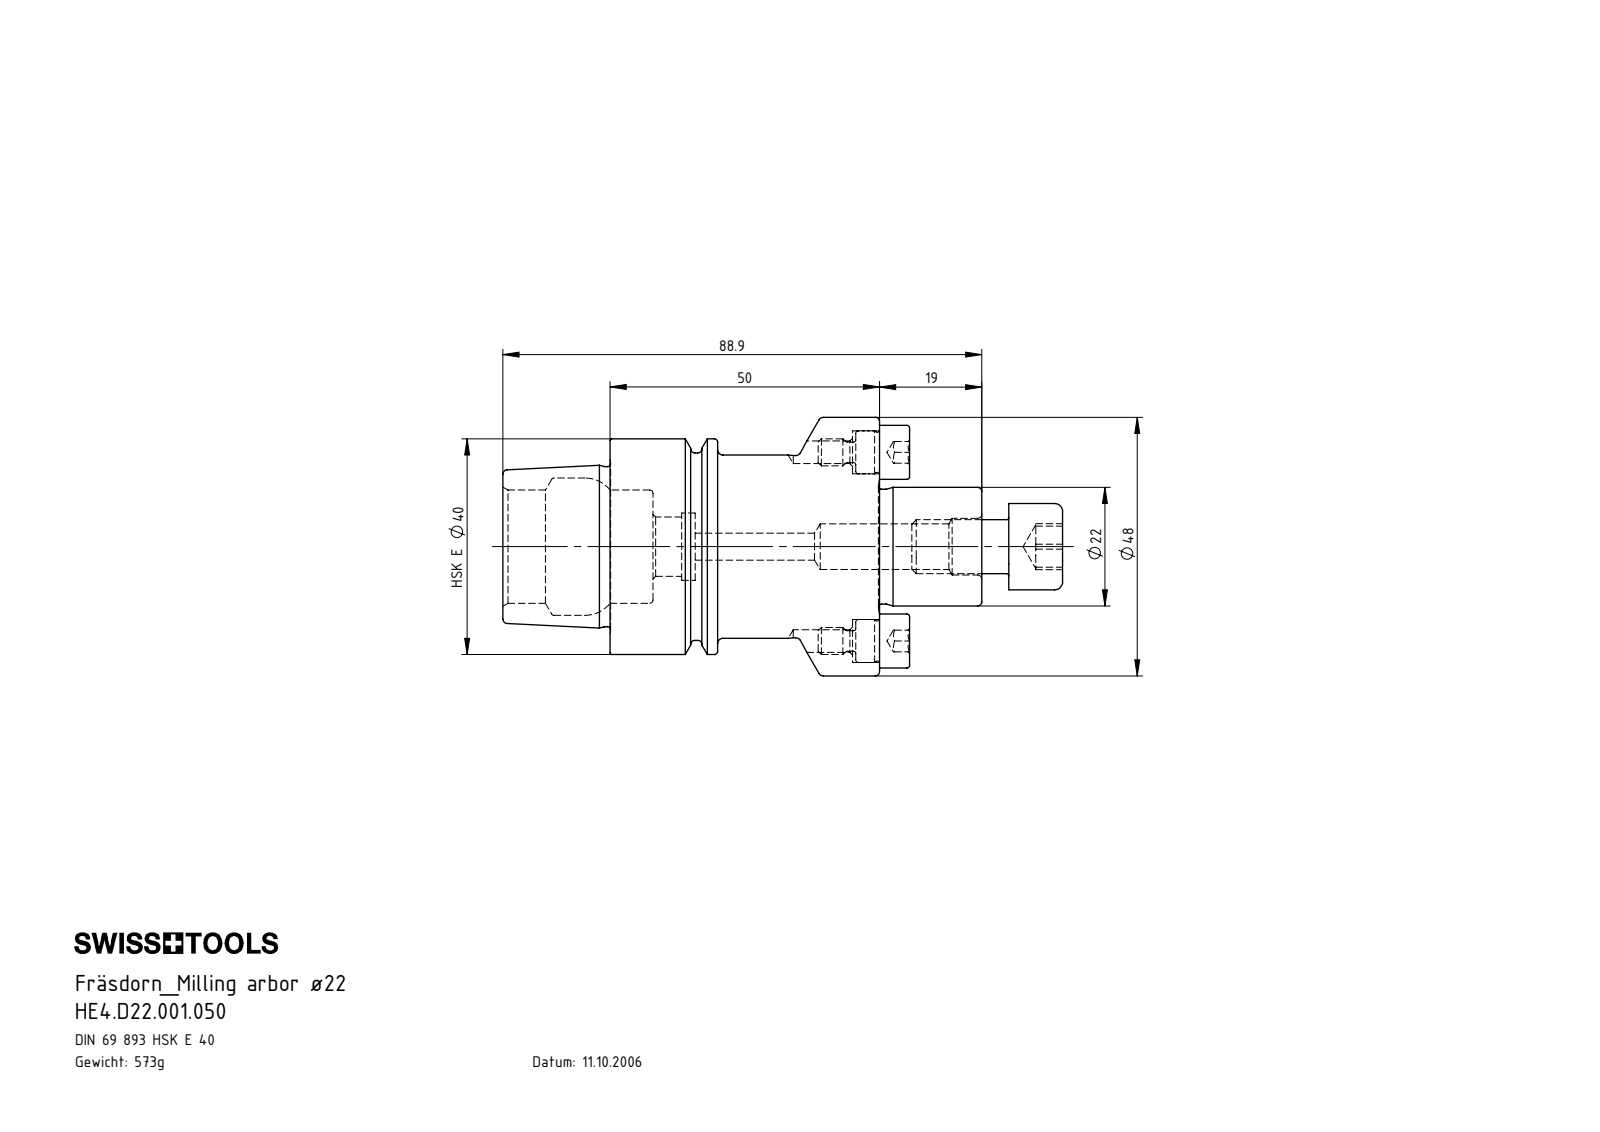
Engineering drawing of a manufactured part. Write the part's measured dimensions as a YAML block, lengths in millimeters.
part_name: "D22-ER1.002.025_A; D22-ER2.001.017_B; HE4.D22.001.050; HE4-D22.001.050_A_Fertigbearbeitung"
step_written_by: "SolidWorks 2017 (CONFIG_CONTROL_DESIGN)"
units: millimeters
bodies: {solids: 4, faces: 239, planar: 47, cylindrical: 60, other: 132}
overall_size: [103.9, 48, 48]
volume: 73024
surface_area: 20136
round_holes:
  - {diameter: 4.2, count: 2}
  - {diameter: 8, count: 2}
  - {diameter: 5, count: 1}
  - {diameter: 8.5, count: 1}
  - {diameter: 10.5, count: 1}
  - {diameter: 11, count: 1}
  - {diameter: 12.5, count: 1}
  - {diameter: 21, count: 1}
  - {diameter: 25.5, count: 1}
round_bosses_or_shafts:
  - {diameter: 10, count: 3}
  - {diameter: 5, count: 2}
  - {diameter: 3.8, count: 2}
  - {diameter: 48, count: 1}
  - {diameter: 40, count: 1}
  - {diameter: 34.75, count: 1}
  - {diameter: 34, count: 1}
  - {diameter: 29.71, count: 1}
face_to_face_distances: [50, 69, 19, 7.95, 42.05, 61.05, 19.9, 27.85, 69.9, 88.9]
hole_center_spacings: [17.5, 35]
